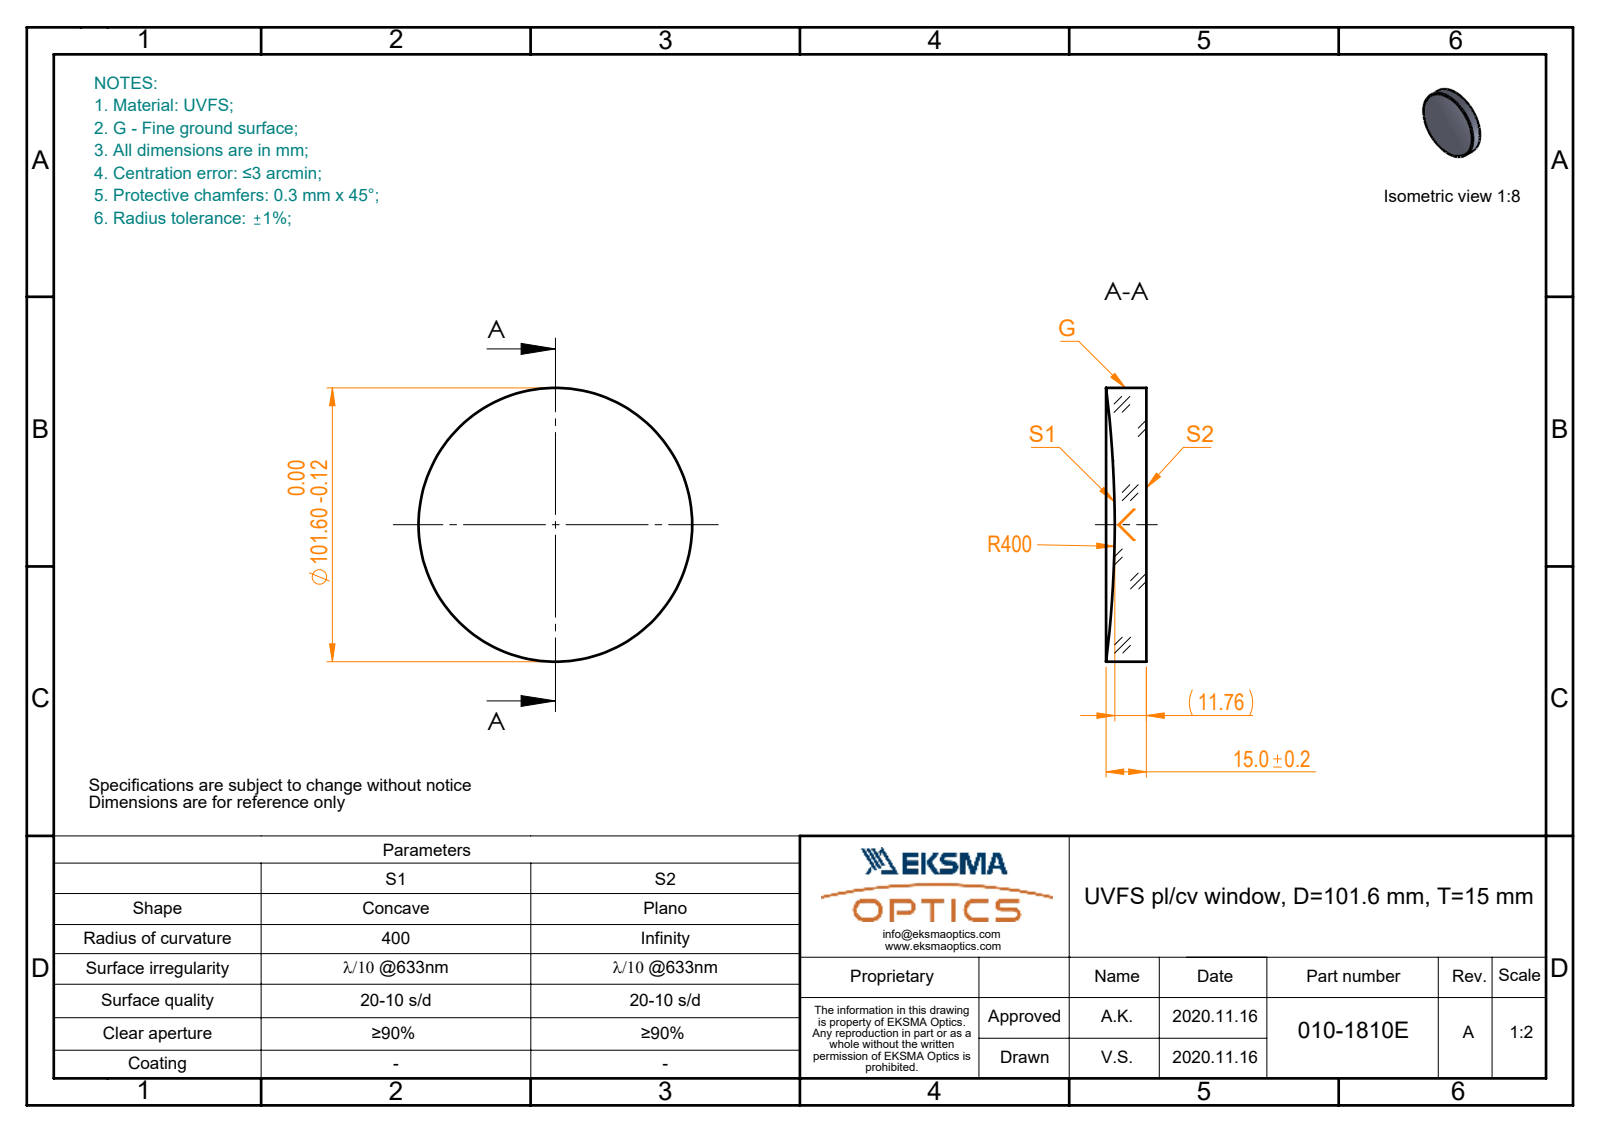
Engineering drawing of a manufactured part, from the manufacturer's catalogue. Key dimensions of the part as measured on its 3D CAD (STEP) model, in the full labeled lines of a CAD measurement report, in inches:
Part name (STEP PRODUCT): 010-1810E_UVFS_PCV_window
STEP written by: SolidWorks 2019 (CONFIG_CONTROL_DESIGN)
Units: inches
Bodies: 1 solid, 5 faces (1 planar, 2 cylindrical, 2 other)
Overall size (bounding box): 4 × 4 × 0.591
Volume: 6.619 in³ · Surface area: 32.6 in²
Round bosses / shafts (diameter × count): ⌀4 ×1
